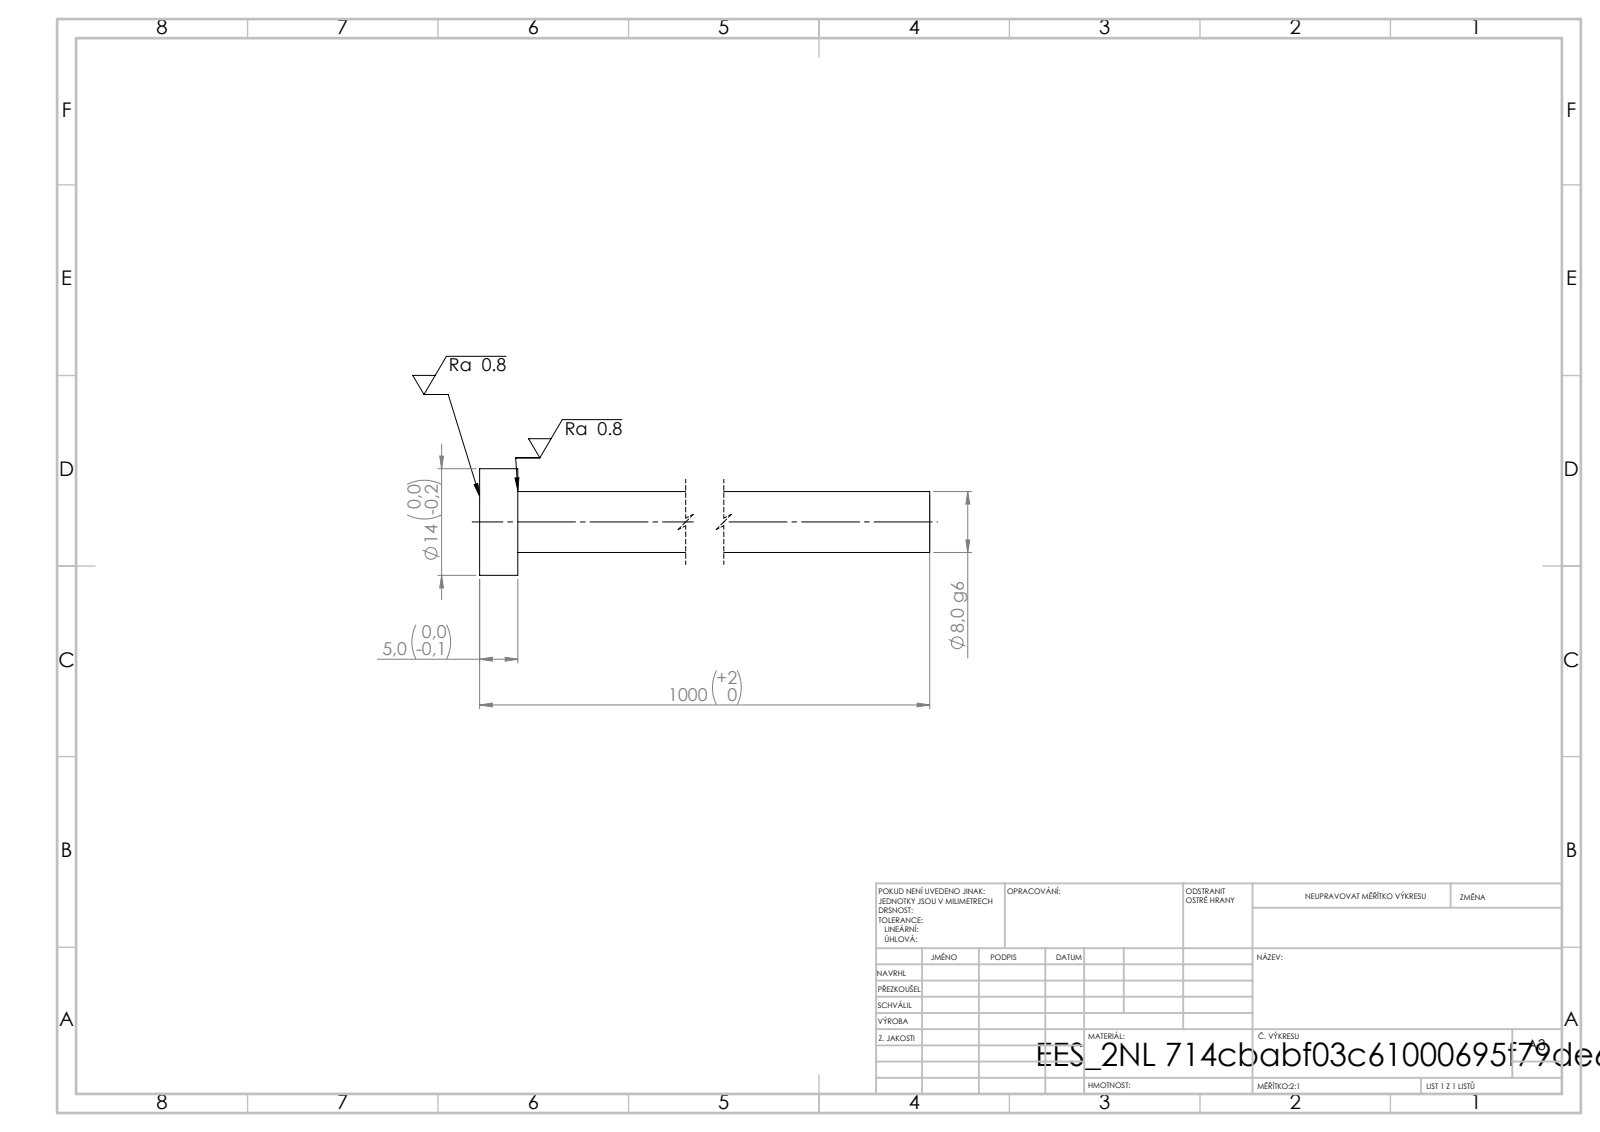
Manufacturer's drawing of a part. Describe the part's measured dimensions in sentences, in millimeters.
Its 3-D file was written by "SolidWorks 2019 (CONFIG_CONTROL_DESIGN)". It is 1 solid with 7 faces: 3 planar, 4 cylindrical and 0 other. Overall it measures 1000 by 14 by 14 millimeters. Its volume is 50 784 cubic millimeters and its surface area 25 535 square millimeters. Round bosses or shafts: 1 of diameter 14, 1 of diameter 8. The main face-to-face distances are 5, 1000, 995.
